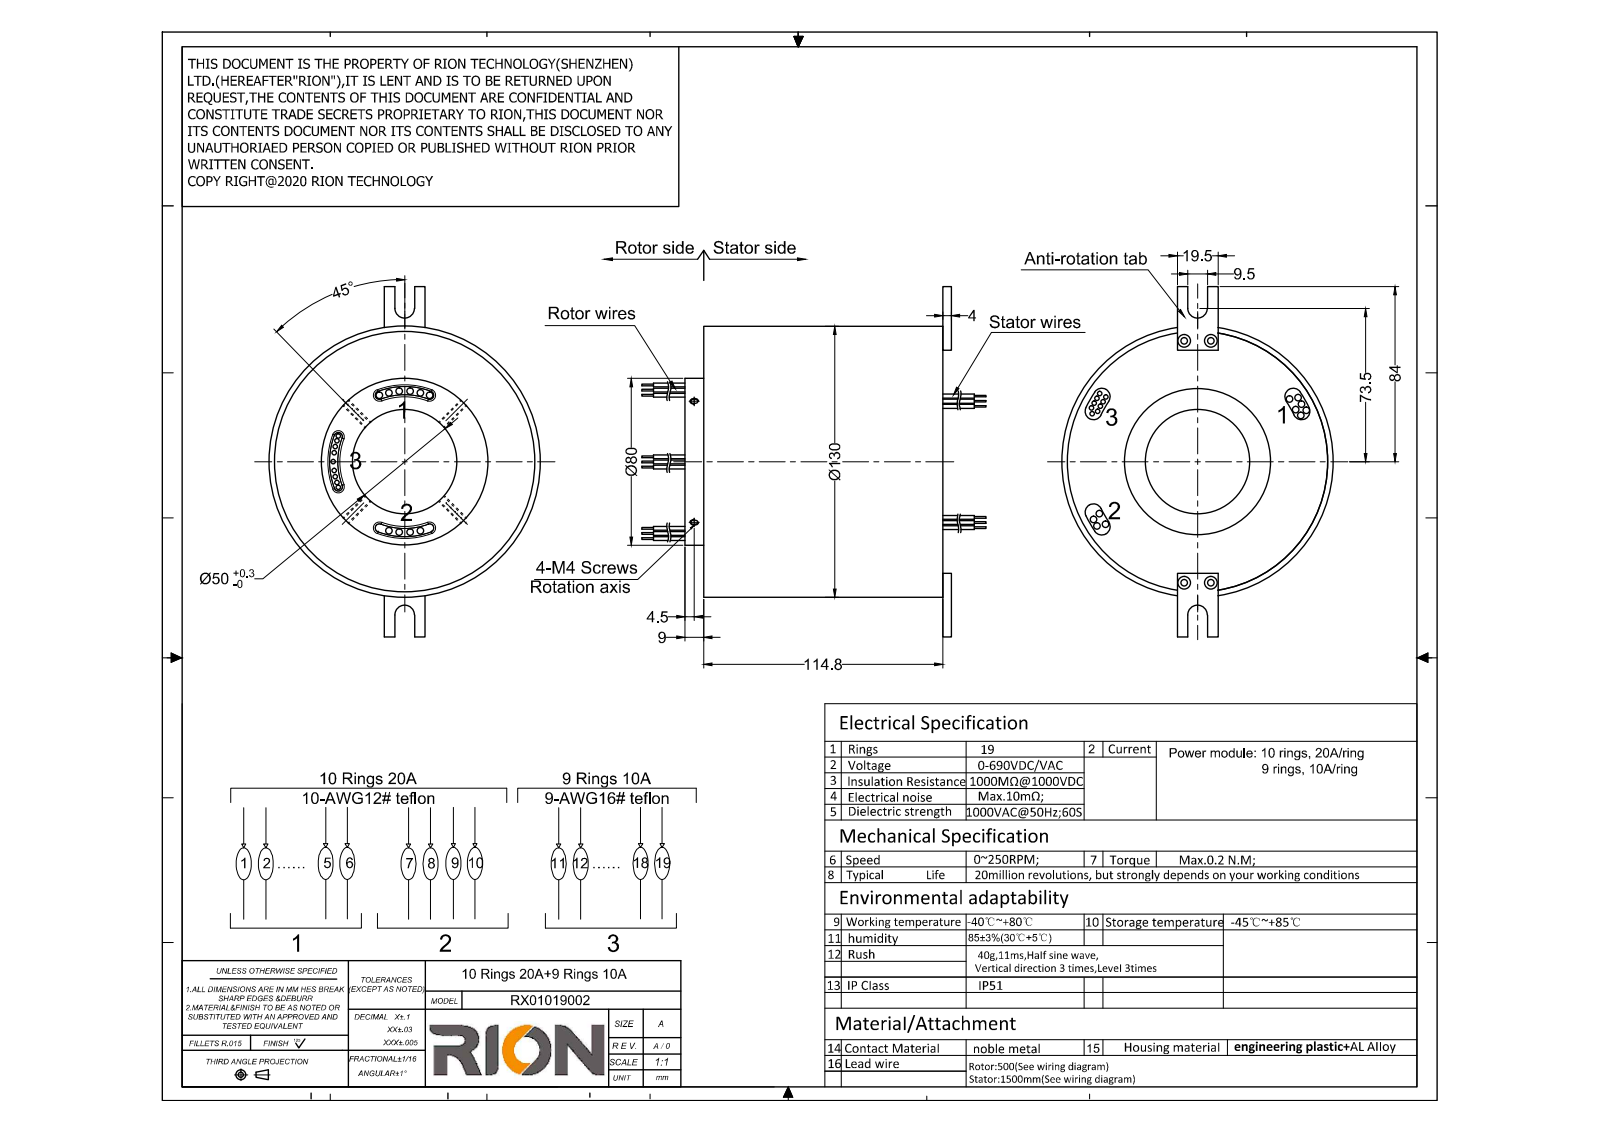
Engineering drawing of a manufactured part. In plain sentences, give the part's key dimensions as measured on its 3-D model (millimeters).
The part is named "RX01019002". Its 3-D file was written by "SolidWorks 2014 (AUTOMOTIVE_DESIGN)". It is 1 solid with 245 faces: 84 planar, 145 cylindrical and 16 other. Overall it measures 181.8 by 168 by 130 millimeters. Its volume is 1 334 000 cubic millimeters and its surface area 110 405 square millimeters. Round holes: 4 of diameter 2.5, 4 of diameter 3.2, 4 of diameter 3.3, 1 of diameter 50, 1 of diameter 70, 1 of diameter 125. Round bosses or shafts: 20 of diameter 3.2, 18 of diameter 2.1, 1 of diameter 130, 1 of diameter 124.8, 1 of diameter 80, 1 of diameter 69.8. Partial cylindrical surfaces (rounded edges, fillets, slot ends): 6 of radius 1.95, 6 of radius 4, 2 of radius 4.75, 1 of radius 32.05, 1 of radius 35.95. The main face-to-face distances are 114.8, 9, 123.8, 127.8, 118.8, 4, 1, 122.8, 121.8, 5. The hole center spacings are 58.35, 12.7, 116, 116.69.
